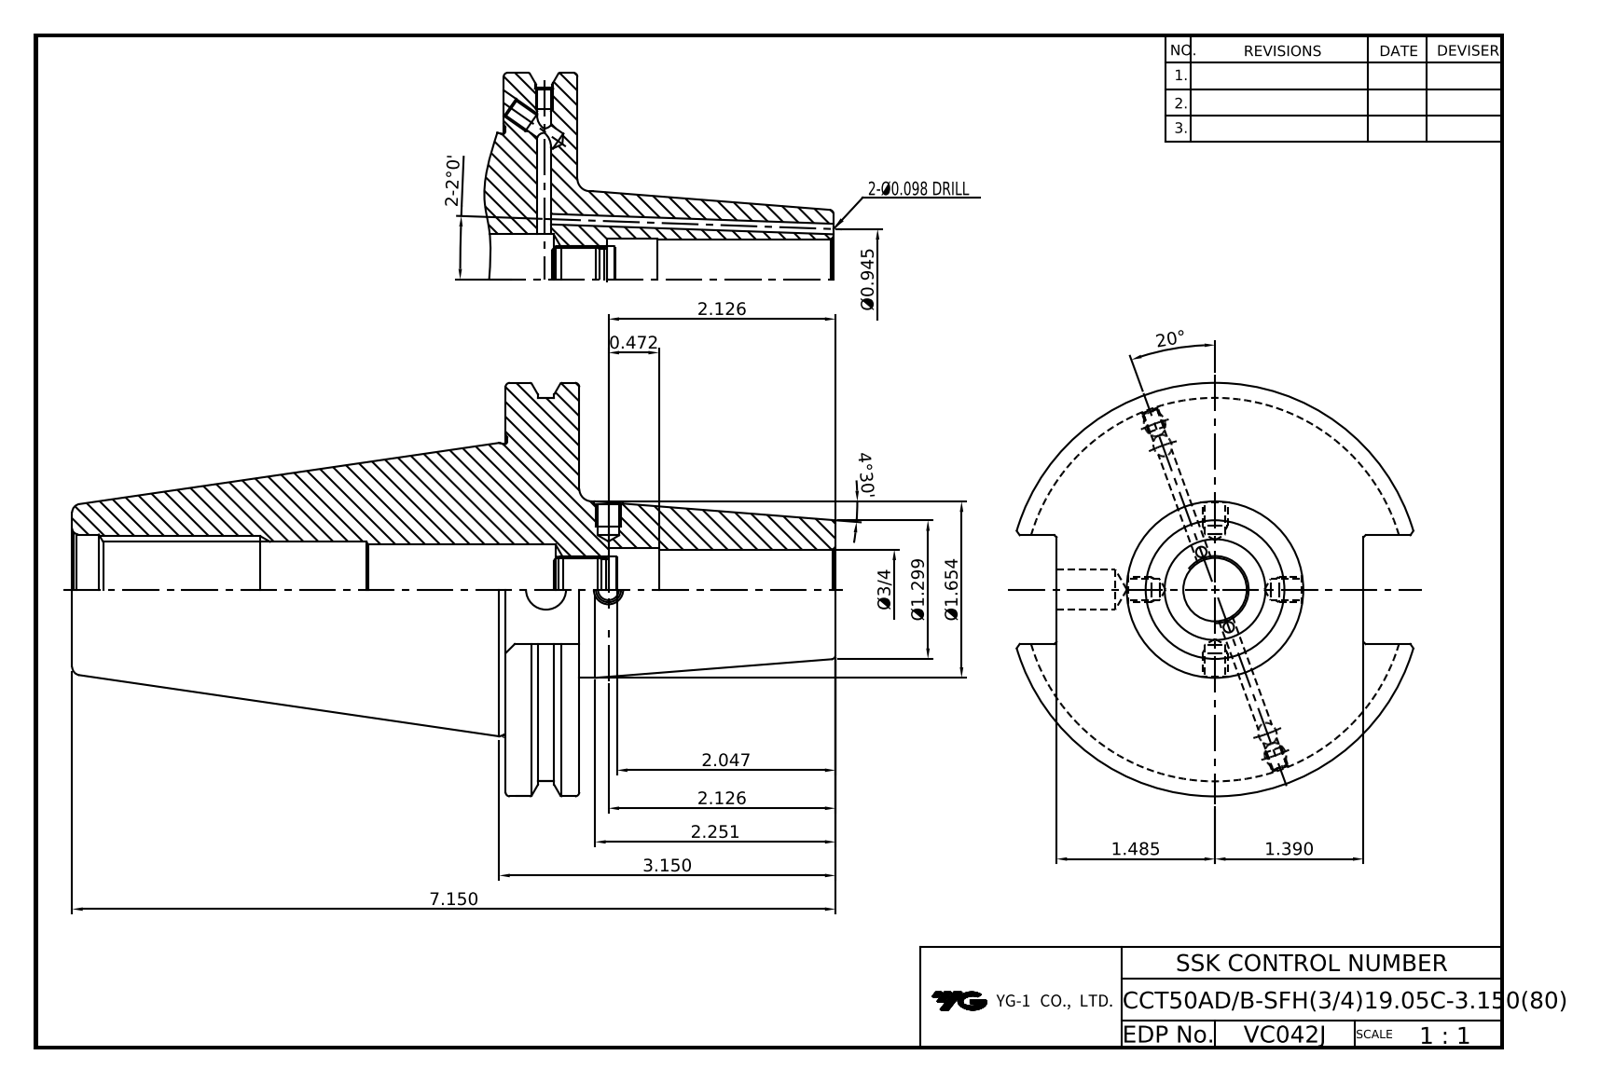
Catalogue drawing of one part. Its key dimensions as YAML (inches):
part_name: "VC042J-CCT50ADB-SFH3_4C-3.15"
step_written_by: "Autodesk Inventor 2020 (AUTOMOTIVE_DESIGN)"
units: inches
bodies: {solids: 1, faces: 88, planar: 38, cylindrical: 27, other: 23}
overall_size: [7.15, 3.875, 3.728]
volume: 22.94
surface_area: 86.3
round_holes:
  - {diameter: 0.128, count: 2}
  - {diameter: 0.163, count: 2}
  - {diameter: 0.165, count: 2}
  - {diameter: 0.197, count: 2}
  - {diameter: 0.375, count: 1}
  - {diameter: 0.587, count: 1}
  - {diameter: 0.75, count: 1}
  - {diameter: 0.774, count: 1}
  - {diameter: 0.846, count: 1}
  - {diameter: 0.865, count: 1}
  - {diameter: 1.031, count: 1}
round_bosses_or_shafts:
  - {diameter: 3.875, count: 1}
  - {diameter: 3.594, count: 1}
  - {diameter: 2.726, count: 1}
  - {diameter: 1.654, count: 1}
face_to_face_distances: [0.691, 4.059, 4.75, 7.15, 3.091, 2.4, 2.875, 1.02, 4.075, 0.016]
